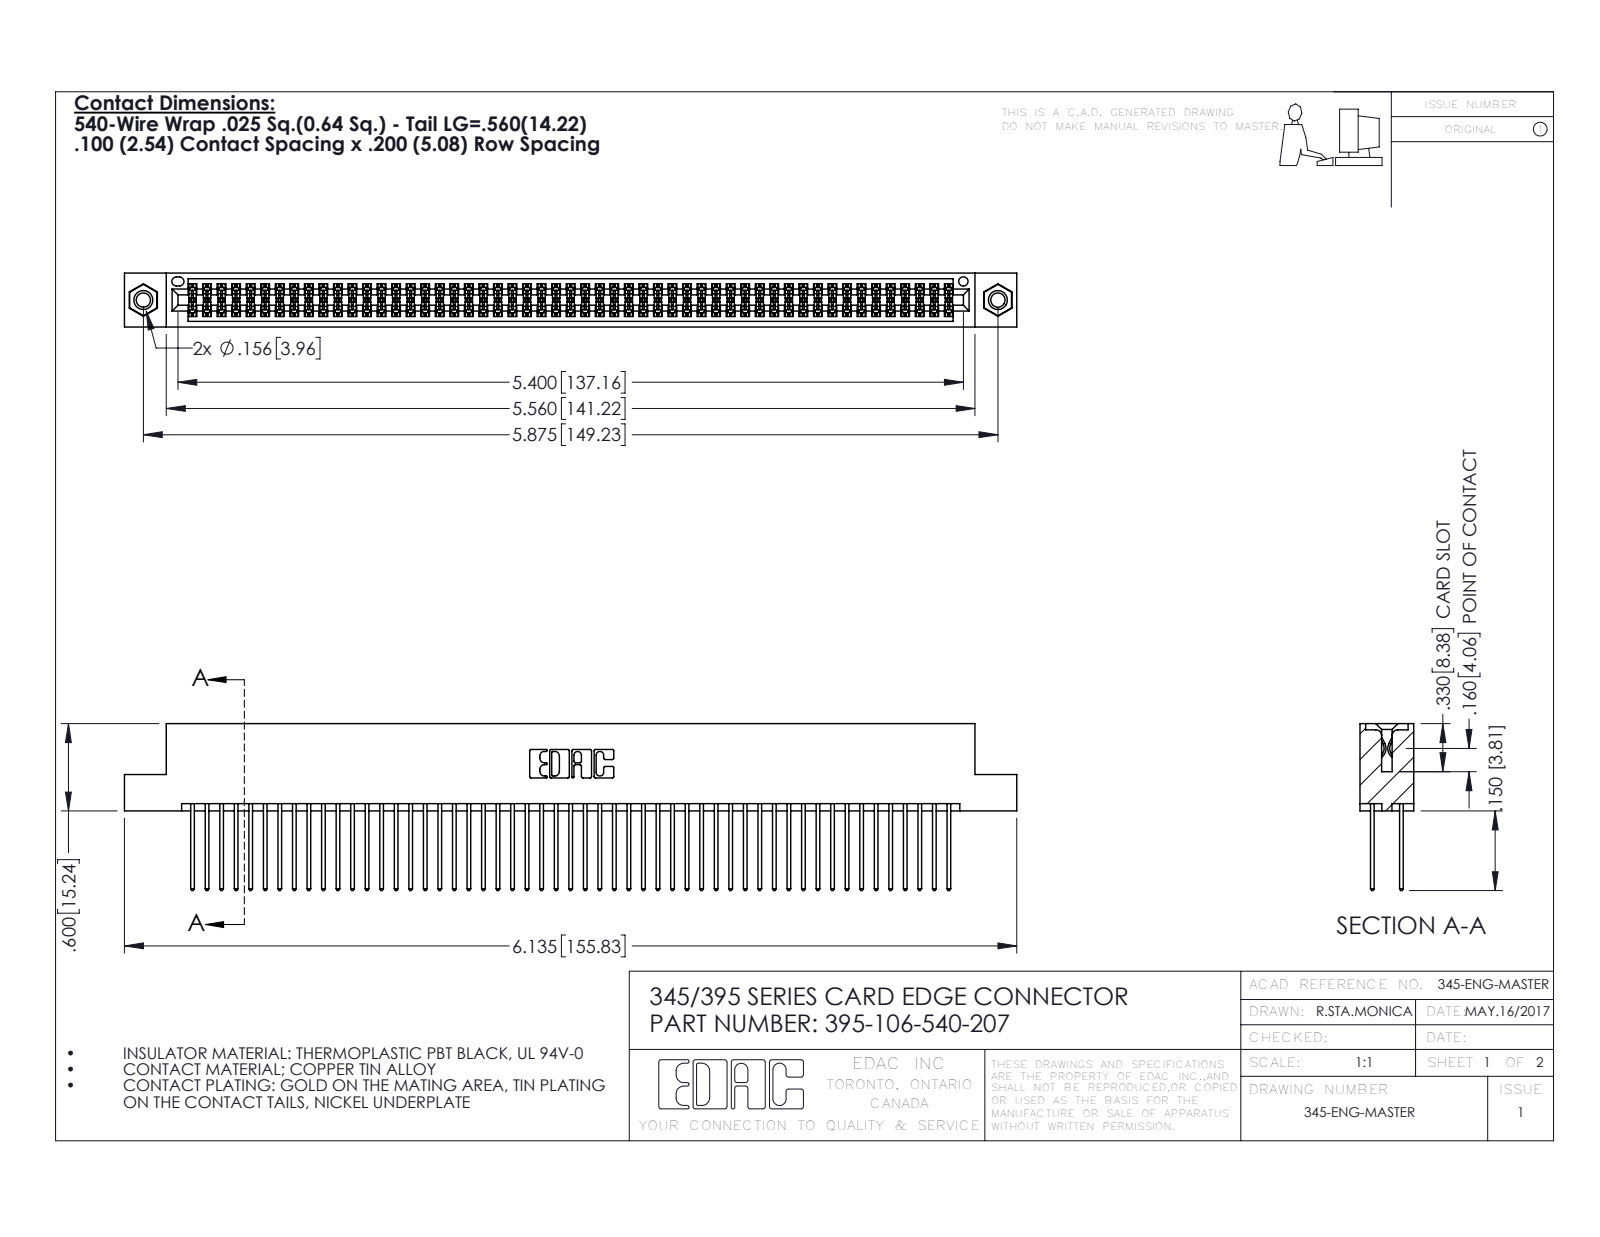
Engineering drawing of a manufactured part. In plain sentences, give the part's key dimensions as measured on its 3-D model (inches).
The part is named "345-250-001_345-250-005-103; 395-106-540-207; 345 Part_Flush Mounting Lugs - 0.156 Dia-TI; 345-292-001_345-293-140". Its 3-D file was written by "SolidWorks 2016 (CONFIG_CONTROL_DESIGN)". It is 109 solids with 5486 faces: 3610 planar, 1860 cylindrical and 16 other. Overall it measures 6.135 by 1.147 by 0.37 inches. Its volume is 0.954 cubic inches and its surface area 39.07 square inches. Round holes: 2 of diameter 0.098, 2 of diameter 0.125, 2 of diameter 0.156, 1 of diameter 0.064. Round bosses or shafts: 2 of diameter 0.155. Partial cylindrical surfaces (rounded edges, fillets, slot ends): 159 of radius 0.006, 106 of radius 0.01, 22 of radius 0.01, 6 of radius 0.007, 6 of radius 0.031, 3 of radius 0.026, 2 of radius 0.014, 2 of radius 0.019. The main face-to-face distances are 0.072, 0.298, 0.2, 0.098, 0.272, 0.025, 0.37, 0.225, 0.175, 0.149. The hole center spacings are 0.27, 5.639, 5.875.
